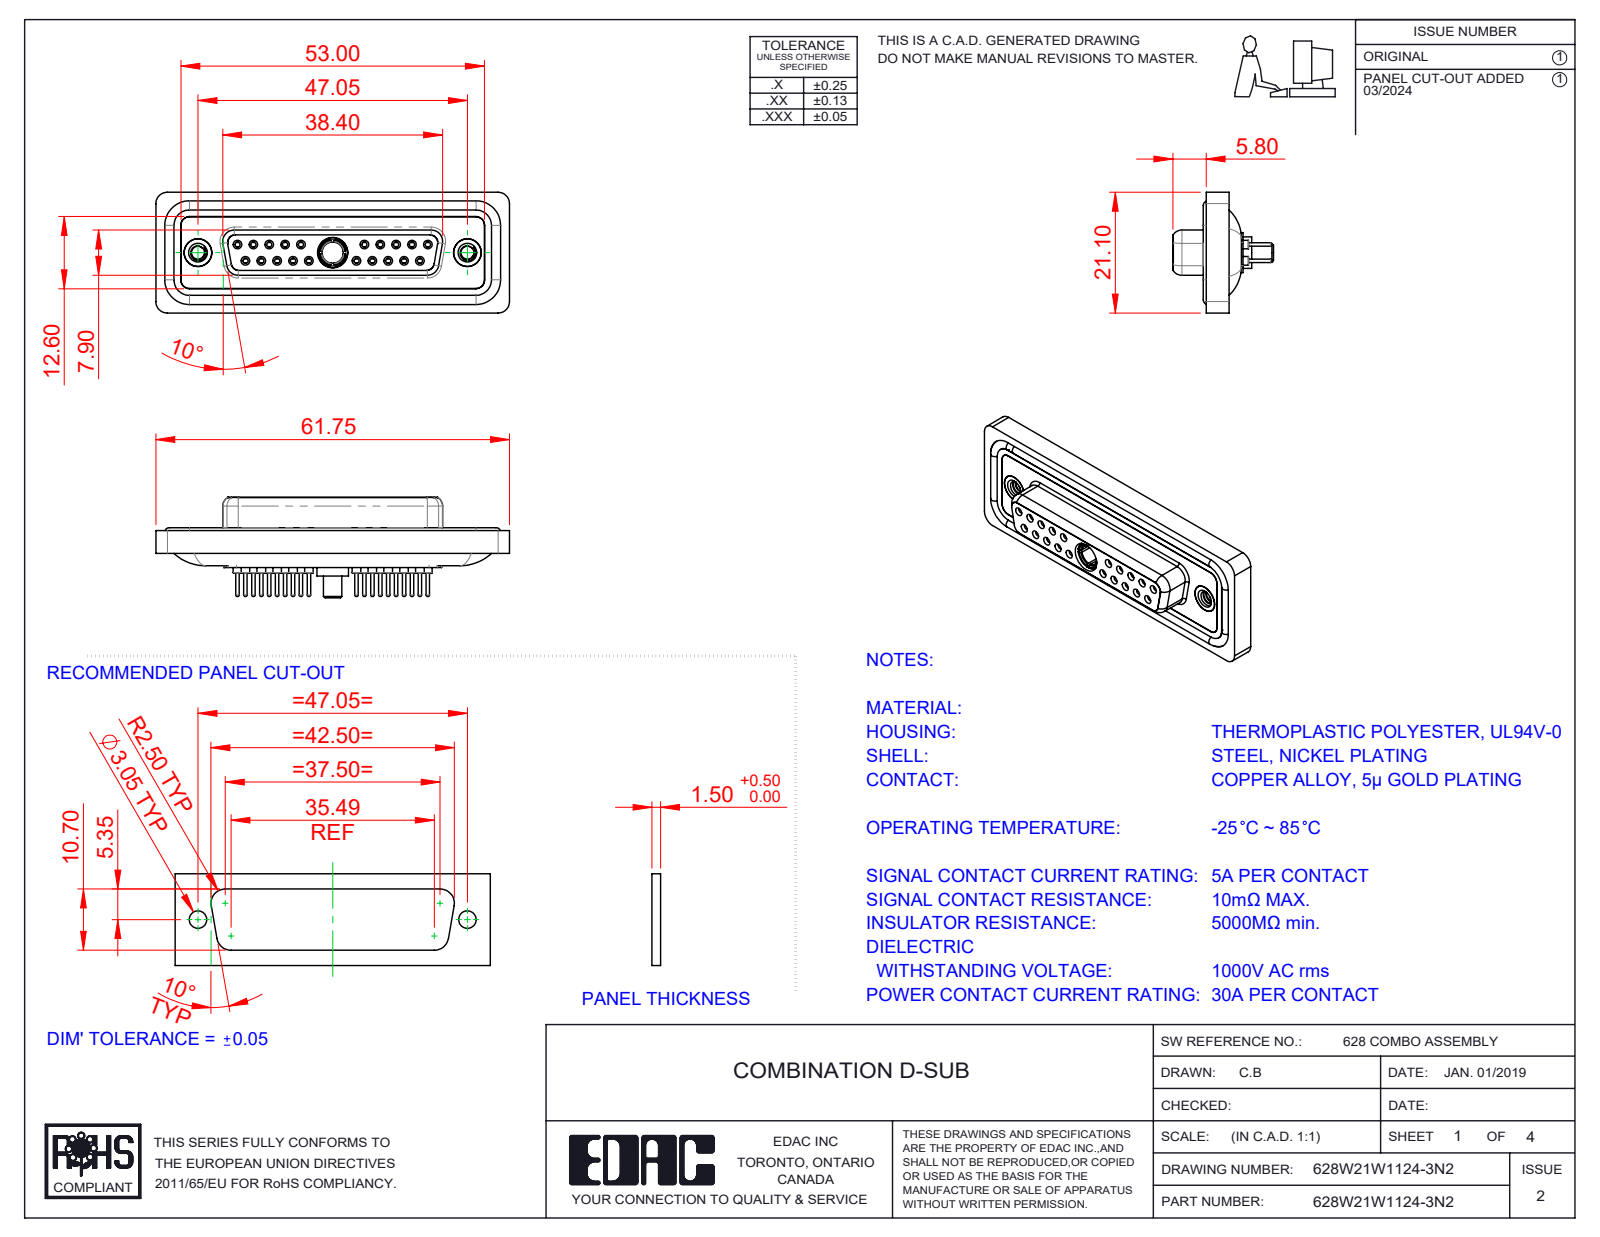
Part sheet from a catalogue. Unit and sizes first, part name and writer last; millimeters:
Units: millimetres
Overall size (bounding box): 61.75 × 21.1 × 17.55
Round holes (diameter × count): ⌀0.9 ×20, ⌀1.1 ×20, ⌀1.5 ×20, ⌀2 ×20, ⌀1.6 ×10, ⌀1.7 ×10, ⌀4.85 ×3, ⌀2.26 ×2, ⌀4 ×2, ⌀4.05 ×2, ⌀5 ×2, ⌀3.7 ×1
Round bosses / shafts (diameter × count): ⌀2.2 ×20, ⌀0.6 ×20, ⌀1.6 ×14, ⌀4.95 ×2, ⌀4.8 ×2, ⌀5.5 ×1, ⌀5.2 ×1, ⌀4.96 ×1
Partial cylindrical surfaces — rounded edges, fillets, slot ends (radius × count): R1.5 ×22, R2 ×18, R1.35 ×8, R1.6 ×8, R0.25 ×4, R0.5 ×4, R0.6 ×4, R0.65 ×4
Main face-to-face distances: 0.4, 1.8, 7.45, 6.6, 5.65, 0.5, 1.6, 7.05, 2.9, 1.1
Hole centre spacings: 3.16, 2.77, 5.54, 5.03, 8.31, 7.48, 16.62, 19.39
Volume: 8 381 mm³ · Surface area: 14 006 mm²
Bodies: 29 solids, 1560 faces (434 planar, 591 cylindrical, 535 other)
Part name (STEP PRODUCT): Power Socket_30A S; 628Combo Waterproof Housing_25 Contacts; 628Combo Housing_21W1; 628Combo Threaded Rivet_2 (+5 more)
STEP written by: SolidWorks 2023 (CONFIG_CONTROL_DESIGN)
